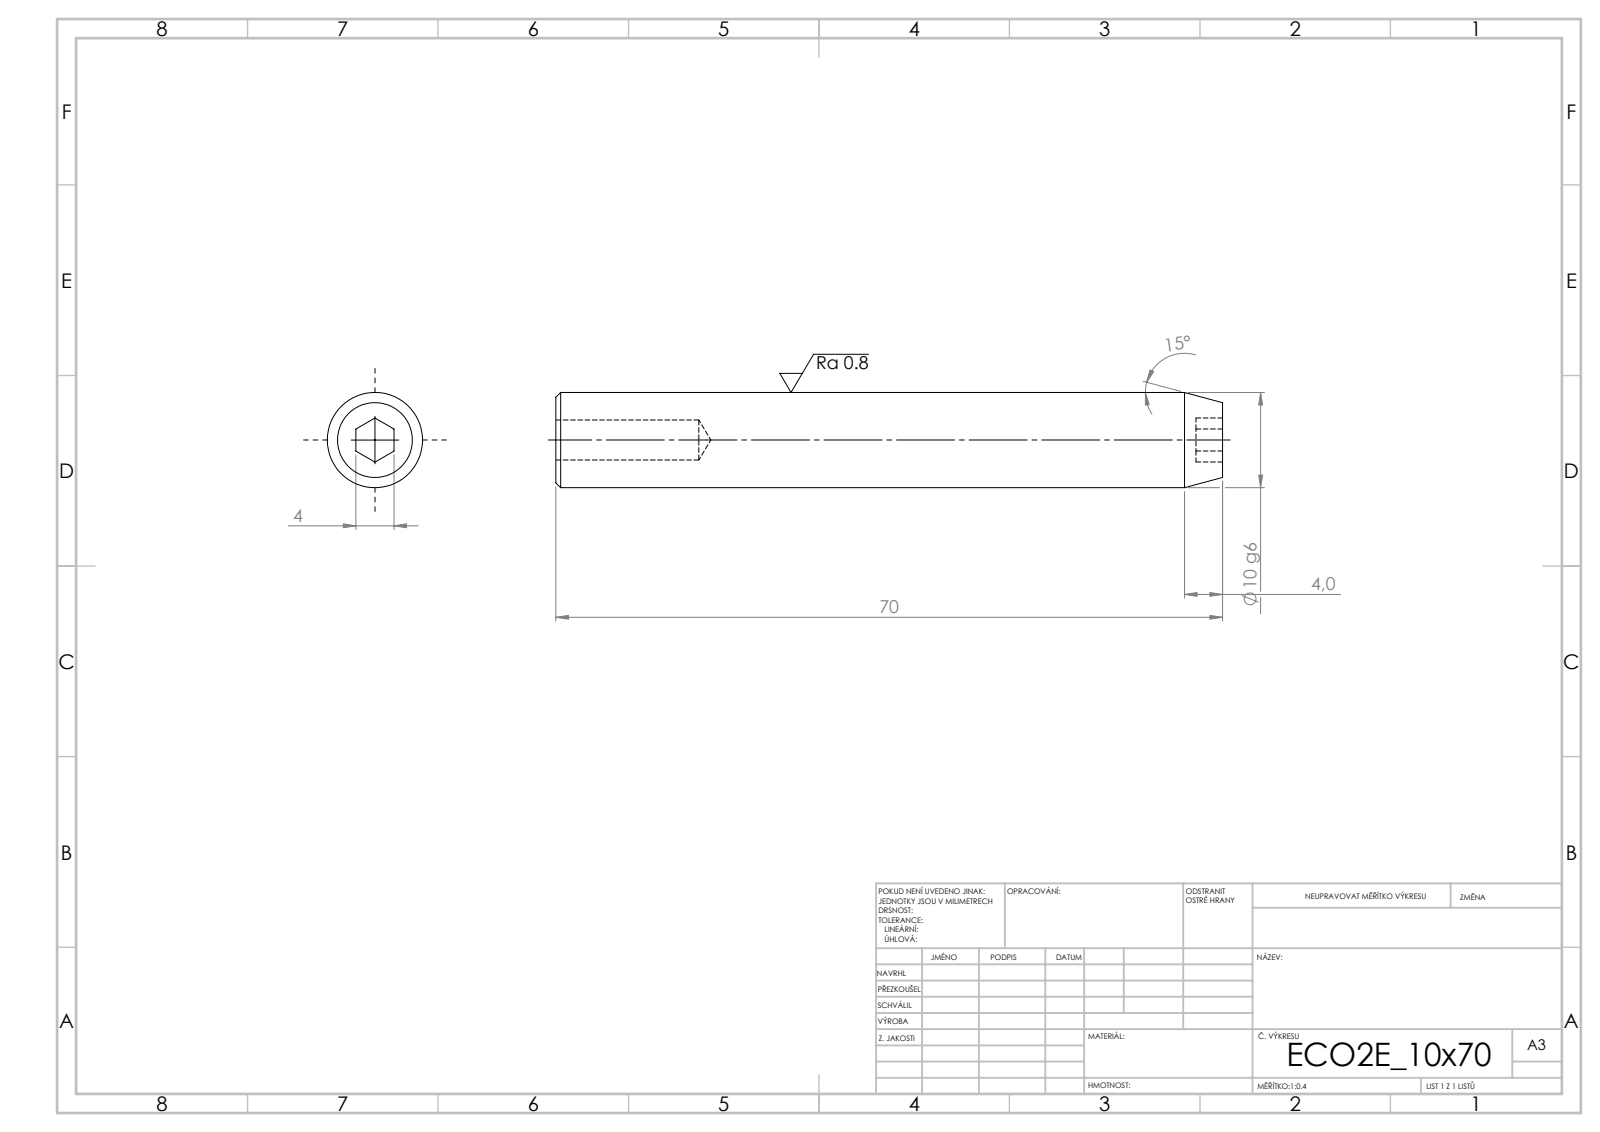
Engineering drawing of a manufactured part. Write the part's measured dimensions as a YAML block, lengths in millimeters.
step_written_by: "SolidWorks 2019 (CONFIG_CONTROL_DESIGN)"
units: millimeters
bodies: {solids: 1, faces: 19, planar: 9, cylindrical: 4, other: 6}
overall_size: [70, 10, 10]
volume: 5179
surface_area: 2546
round_holes:
  - {diameter: 4.2, count: 1}
round_bosses_or_shafts:
  - {diameter: 10, count: 1}
face_to_face_distances: [70, 4, 2.8, 67.2]
